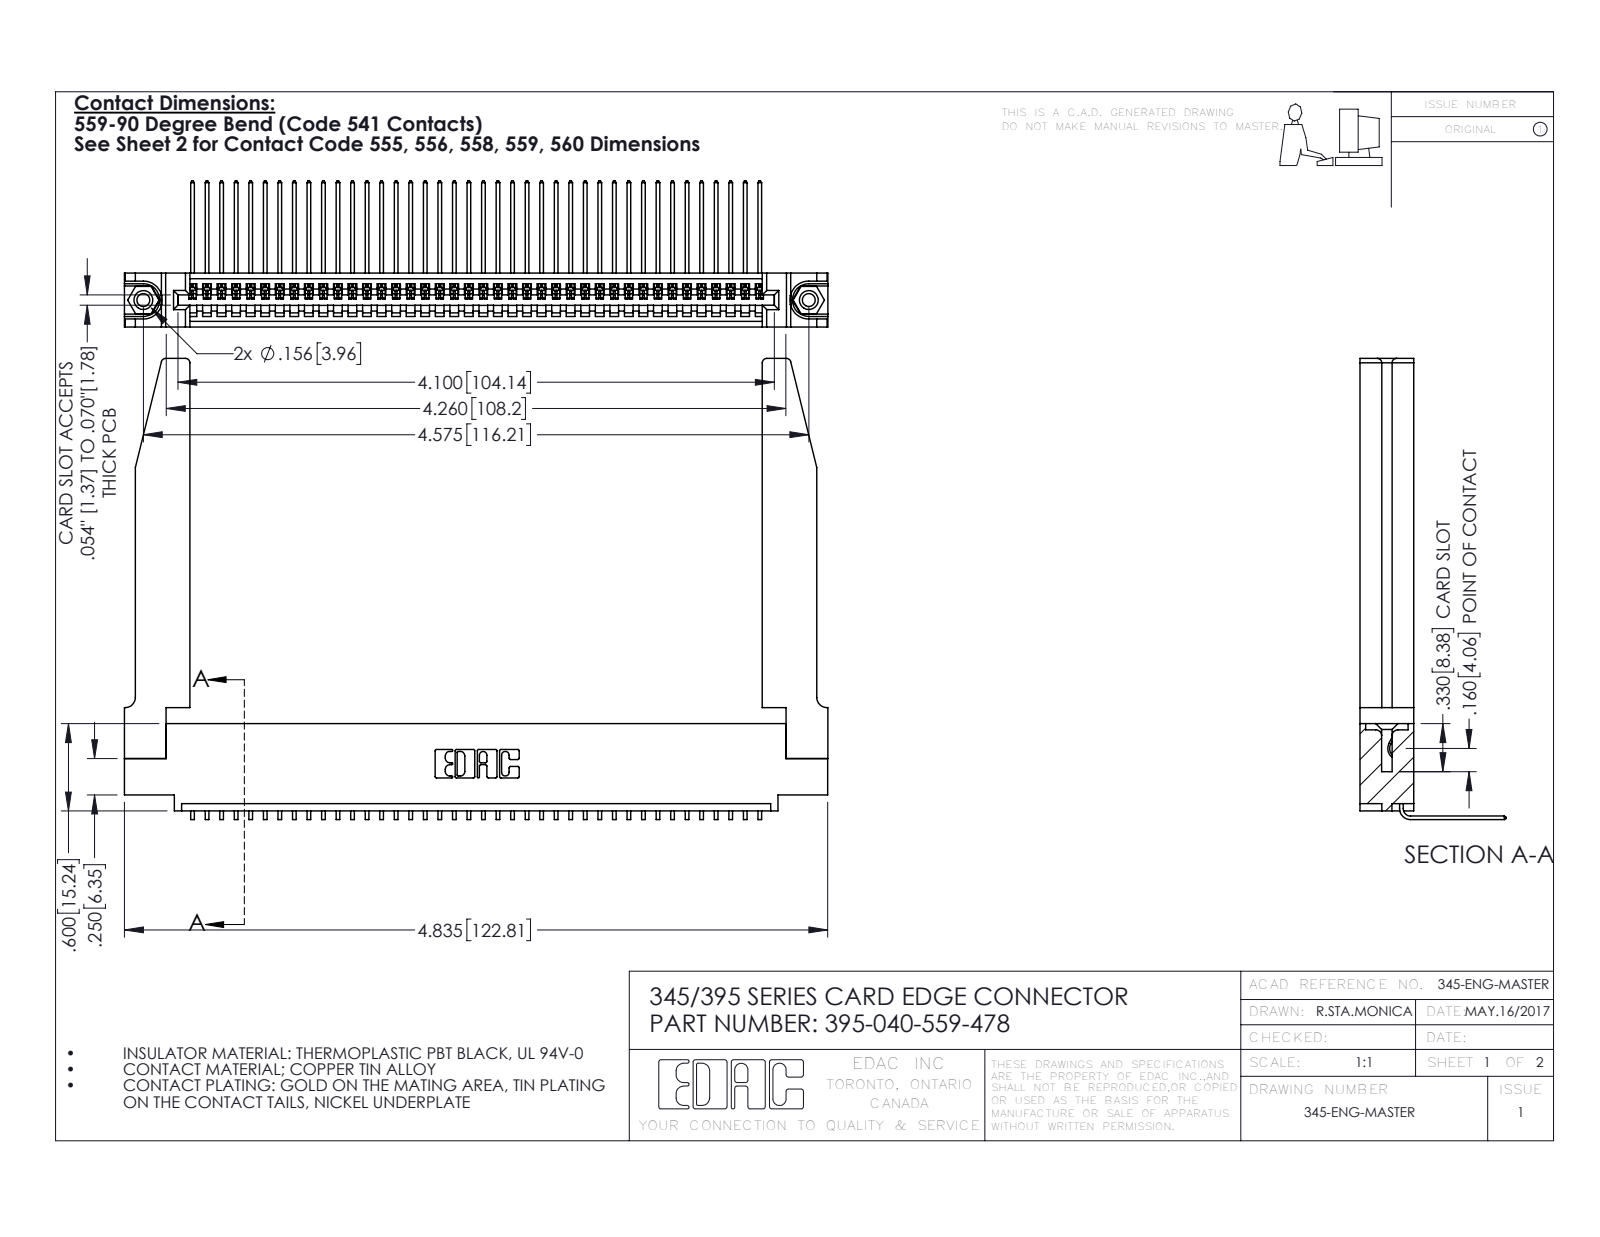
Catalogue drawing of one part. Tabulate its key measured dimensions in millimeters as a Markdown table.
| quantity | value |
| --- | --- |
| part name | 345-250-001_345-250-001-102; 345 Part_0.110 Offset - 0.156 Dia-TH; 345-292-001_558 559 Tail - 1; 395-040-559-478 (+1 more) |
| STEP written by | SolidWorks 2016 (CONFIG_CONTROL_DESIGN) |
| units | millimeters |
| bodies | 45 solids, 2764 faces (1906 planar, 806 cylindrical, 52 other) |
| overall size | 122.8 × 80.5 × 25.5 |
| volume | 19 480 mm³ |
| surface area | 23 250 mm² |
| round holes (diameter × count) | 2.3 × 2, 3.2 × 2, 4 × 2, 1.6 × 1 |
| round bosses / shafts (diameter × count) | 3.9 × 2 |
| partial cylindrical surfaces (radius × count) | 0.2 × 80, 0.3 × 22, 0.8 × 8, 0.2 × 6, 0.8 × 6, 0.7 × 3, 0.8 × 2, 1 × 2 |
| main face-to-face distances | 9.4, 1.8, 7.6, 5.1, 2.5, 6.9, 0.6, 5.7, 3.8, 3.8 |
| hole center spacings | 6.9, 110.2, 116.2 |
